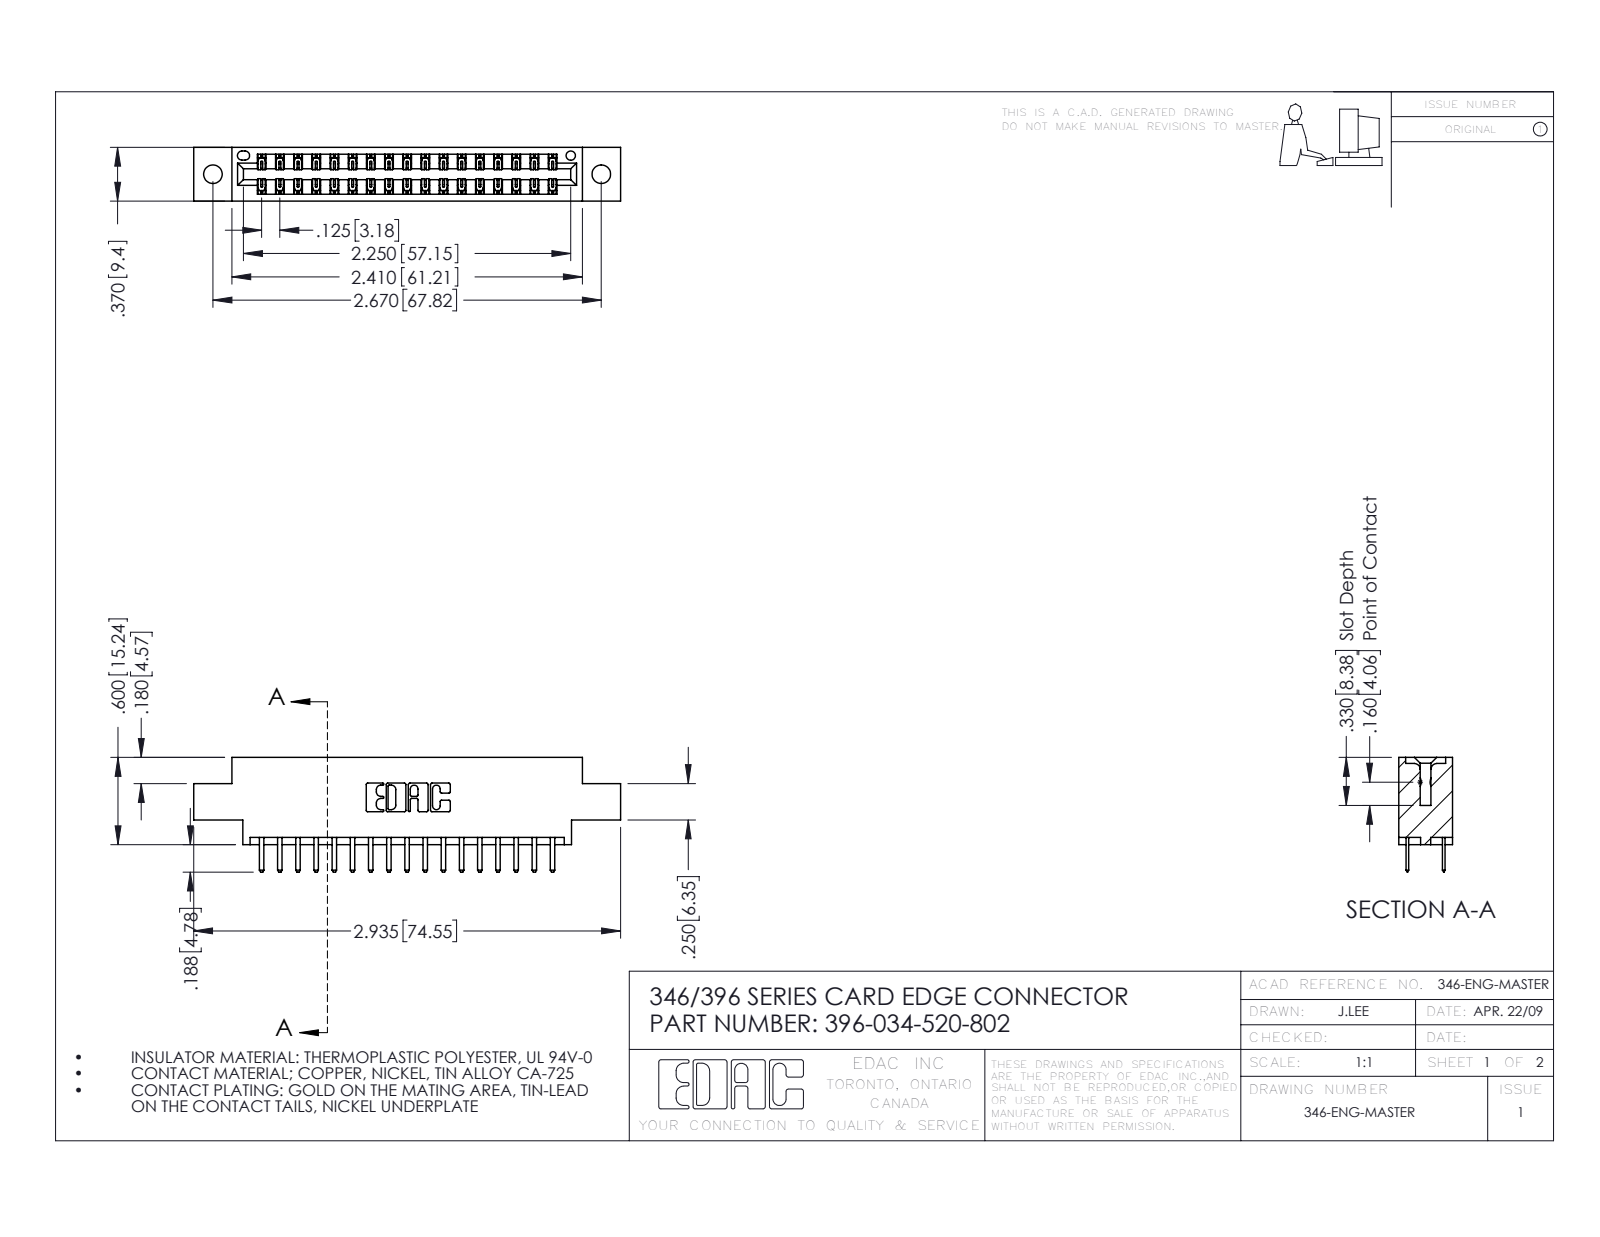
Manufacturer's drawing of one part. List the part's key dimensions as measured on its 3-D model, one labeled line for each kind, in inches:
Part name (STEP PRODUCT): 346 Part_0.170 Offset - 0.128 Dia; 396-034-520-802; 345-292-001_345-293-120
STEP written by: SolidWorks 2016 (CONFIG_CONTROL_DESIGN)
Units: inches
Bodies: 35 solids, 2030 faces (1338 planar, 692 cylindrical, 0 other)
Overall size (bounding box): 2.935 × 0.788 × 0.37
Volume: 0.419 in³ · Surface area: 13.83 in²
Round holes (diameter × count): ⌀0.128 ×2, ⌀0.064 ×1
Partial cylindrical surfaces — rounded edges, fillets, slot ends (radius × count): R0.006 ×51, R0.01 ×38, R0.01 ×22, R0.007 ×6, R0.031 ×6, R0.026 ×3, R0.014 ×2, R0.022 ×2
Main face-to-face distances: 0.25, 0.048, 0.322, 0.37, 0.275, 0.072, 0.298, 0.025, 0.148, 0.222
Hole centre spacings: 0.246, 2.463, 2.67
